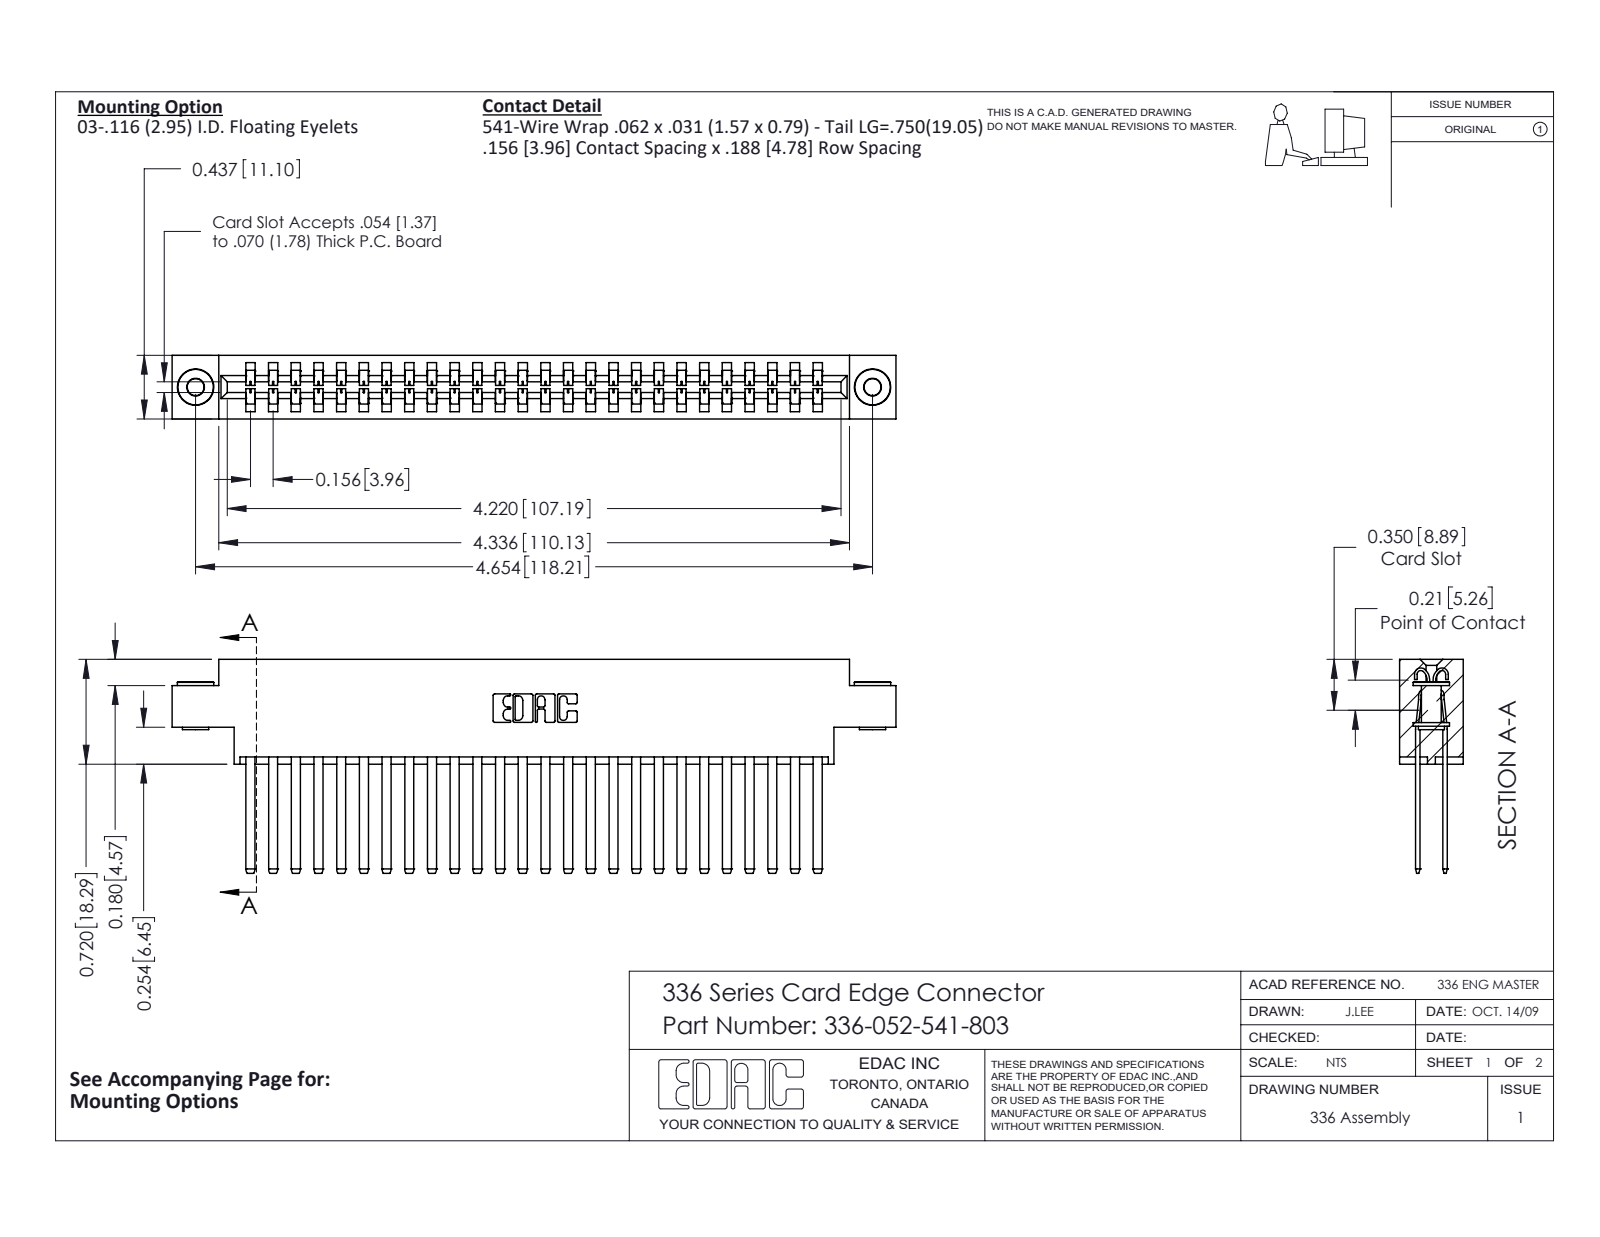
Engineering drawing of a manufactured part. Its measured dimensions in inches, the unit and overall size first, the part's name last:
Units: inches
Overall size (bounding box): 4.977 × 1.47 × 0.437
Round holes (diameter × count): ⌀0.116 ×2, ⌀0.156 ×2
Round bosses / shafts (diameter × count): ⌀0.25 ×2, ⌀0.18 ×2, ⌀0.136 ×2
Partial cylindrical surfaces — rounded edges, fillets, slot ends (radius × count): R0.004 ×104, R0.056 ×52, R0.01 ×22, R0.007 ×6, R0.031 ×6, R0.022 ×4, R0.04 ×4, R0.026 ×3
Main face-to-face distances: 0.188, 0.031, 0.328, 0.14, 0.297, 0.109, 0.437, 0.033, 0.181, 0.256
Hole centre spacings: 4.654
Volume: 1.161 in³ · Surface area: 37.71 in²
Bodies: 55 solids, 2340 faces (1436 planar, 896 cylindrical, 8 other)
Part name (STEP PRODUCT): 336-290-001_336-290-541; 336 Part_Offset - .156 Dia - TH; 345-250-002_345-250-002-102; 336-052-541-803
STEP written by: SolidWorks 2020 (CONFIG_CONTROL_DESIGN)
